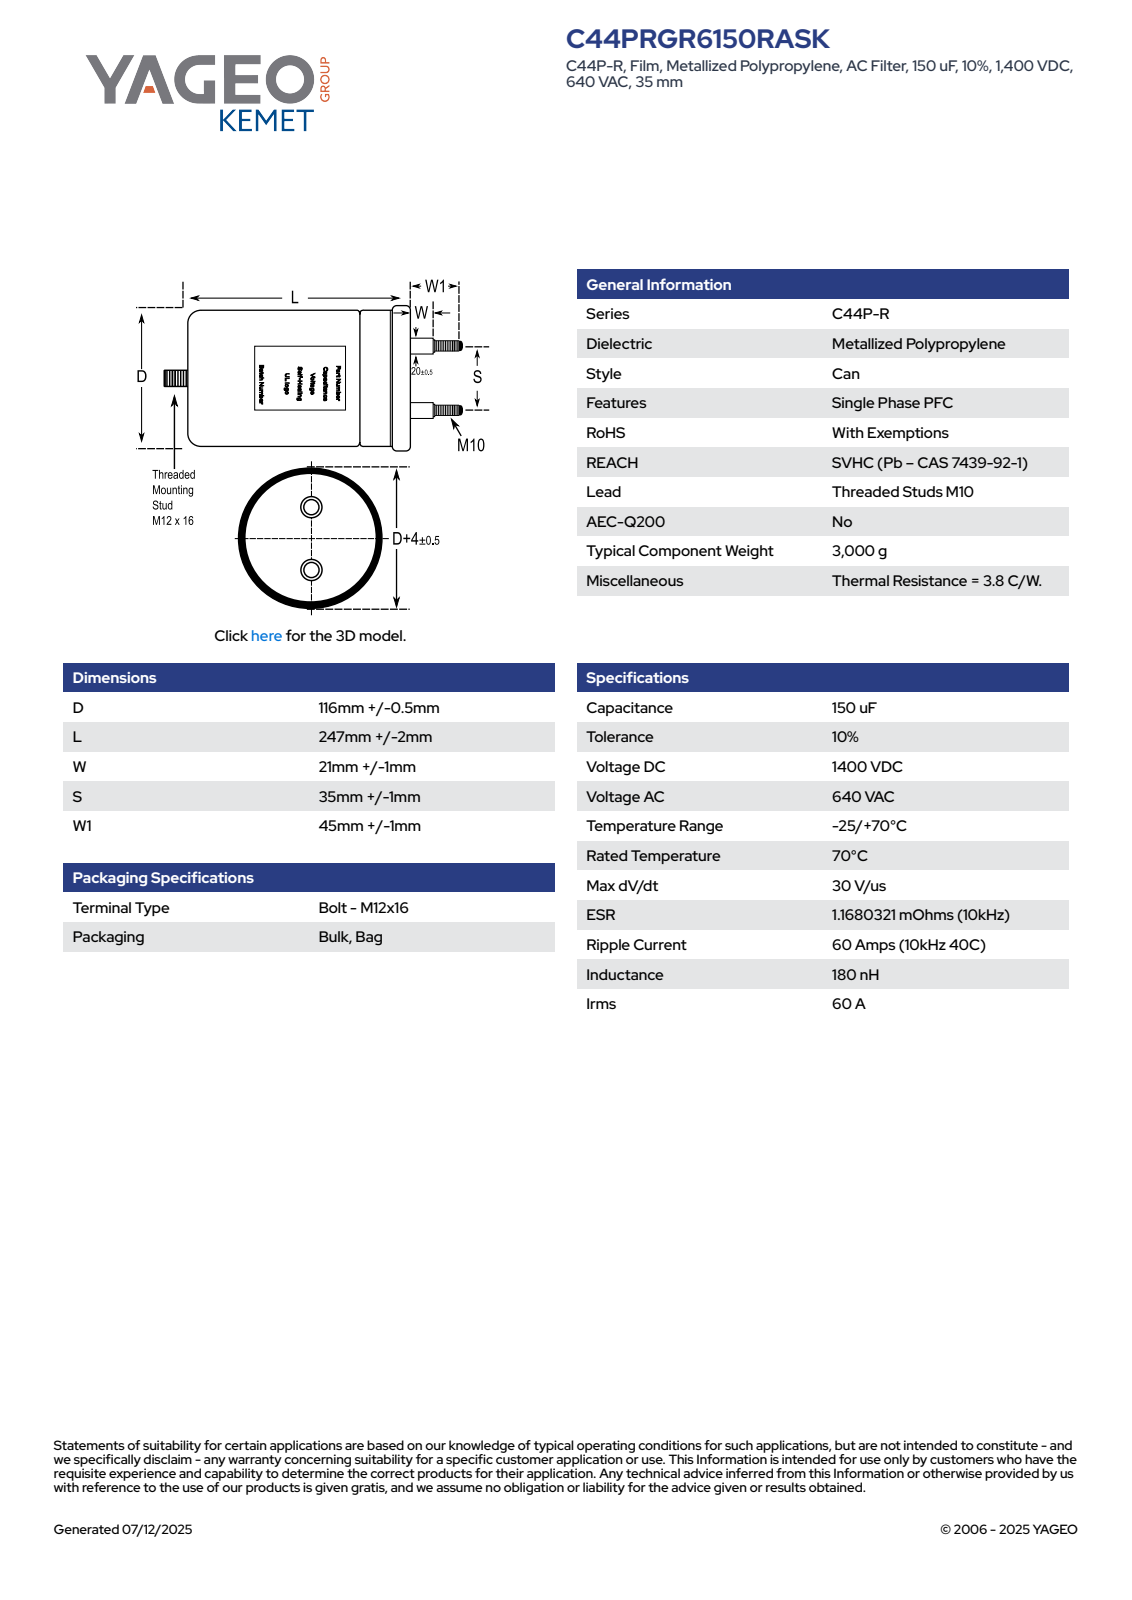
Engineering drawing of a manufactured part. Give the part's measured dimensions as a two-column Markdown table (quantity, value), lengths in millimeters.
| quantity | value |
| --- | --- |
| part name | CFP_C44P_116X247_D116.5L249S35 |
| STEP written by | SolidWorks 2014 (AUTOMOTIVE_DESIGN) |
| units | millimeters |
| bodies | 1 solid, 105 faces (32 planar, 36 cylindrical, 37 other) |
| overall size | 311 × 121 × 121 |
| volume | 2 679 000 mm³ |
| surface area | 118 015 mm² |
| round bosses / shafts (diameter × count) | 12 × 3, 20.5 × 2, 10 × 2, 121 × 1, 116.5 × 1 |
| partial cylindrical surfaces (radius × count) | 58.26 × 1 |
| main face-to-face distances | 249, 241.01, 7.99, 270, 28.99, 21, 295, 53.99, 46, 25 |
